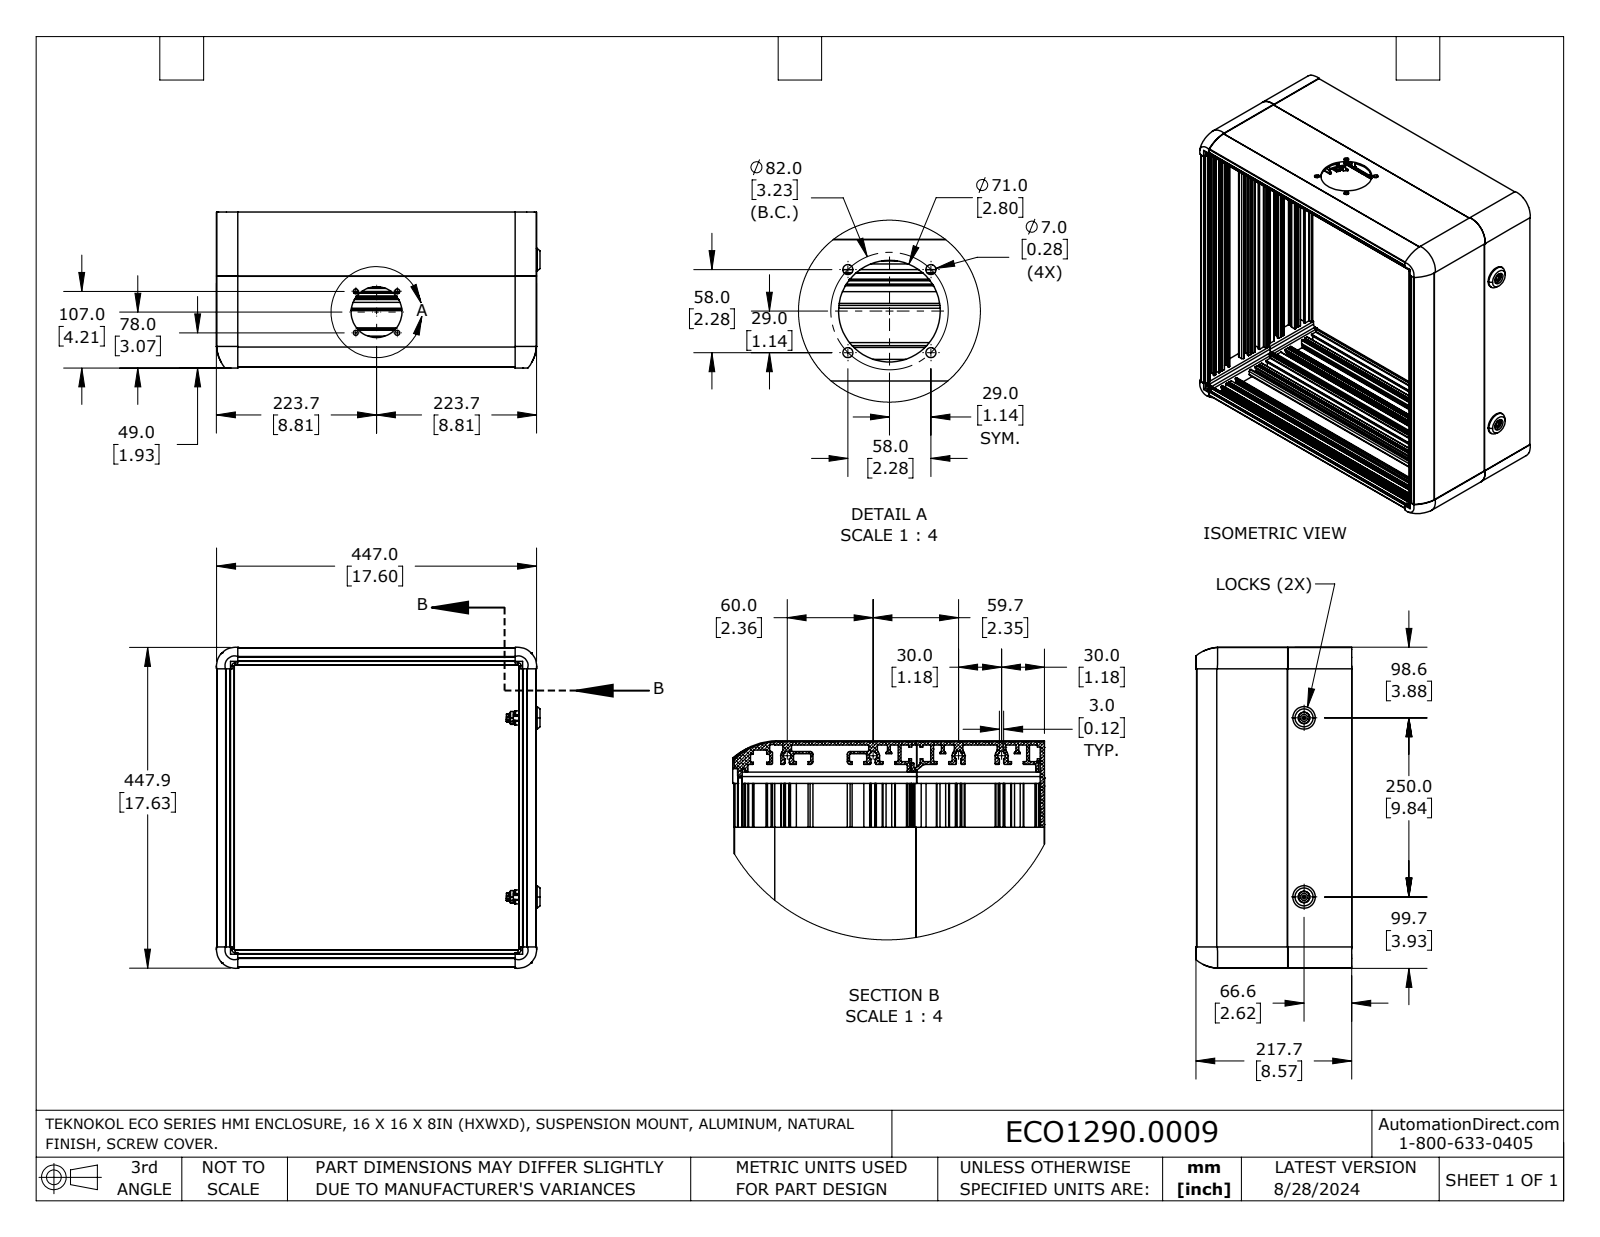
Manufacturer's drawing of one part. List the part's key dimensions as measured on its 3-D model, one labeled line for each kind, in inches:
Part name (STEP PRODUCT): ECO.1290.0009(400x400)_REV1
STEP written by: SolidWorks 2023 (AUTOMOTIVE_DESIGN)
Units: inches
Bodies: 27 solids, 2595 faces (1291 planar, 998 cylindrical, 306 other)
Overall size (bounding box): 17.795 × 17.652 × 8.576
Volume: 192 in³ · Surface area: 3 290 in²
Round holes (diameter × count): ⌀0.205 ×4, ⌀0.276 ×4, ⌀0.197 ×2, ⌀0.236 ×2, ⌀0.237 ×2, ⌀0.394 ×2, ⌀0.478 ×2, ⌀0.63 ×2, ⌀2.795 ×1
Round bosses / shafts (diameter × count): ⌀0.374 ×4, ⌀1.24 ×2, ⌀0.624 ×2, ⌀0.583 ×2, ⌀0.531 ×2, ⌀0.51 ×2, ⌀0.508 ×2, ⌀0.386 ×2
Partial cylindrical surfaces — rounded edges, fillets, slot ends (radius × count): R0.02 ×376, R0.039 ×76, R0.008 ×48, R0.079 ×48, R0.01 ×24, R0.016 ×20, R0.177 ×17, R0.104 ×16
Main face-to-face distances: 17.453, 0.089, 0.118, 17.542, 17.365, 0.531, 0.079, 0.62, 16.922, 16.833
Hole centre spacings: 0.666, 1.615, 1.754, 2.283, 9.843, 1.181, 1.344, 3.229
